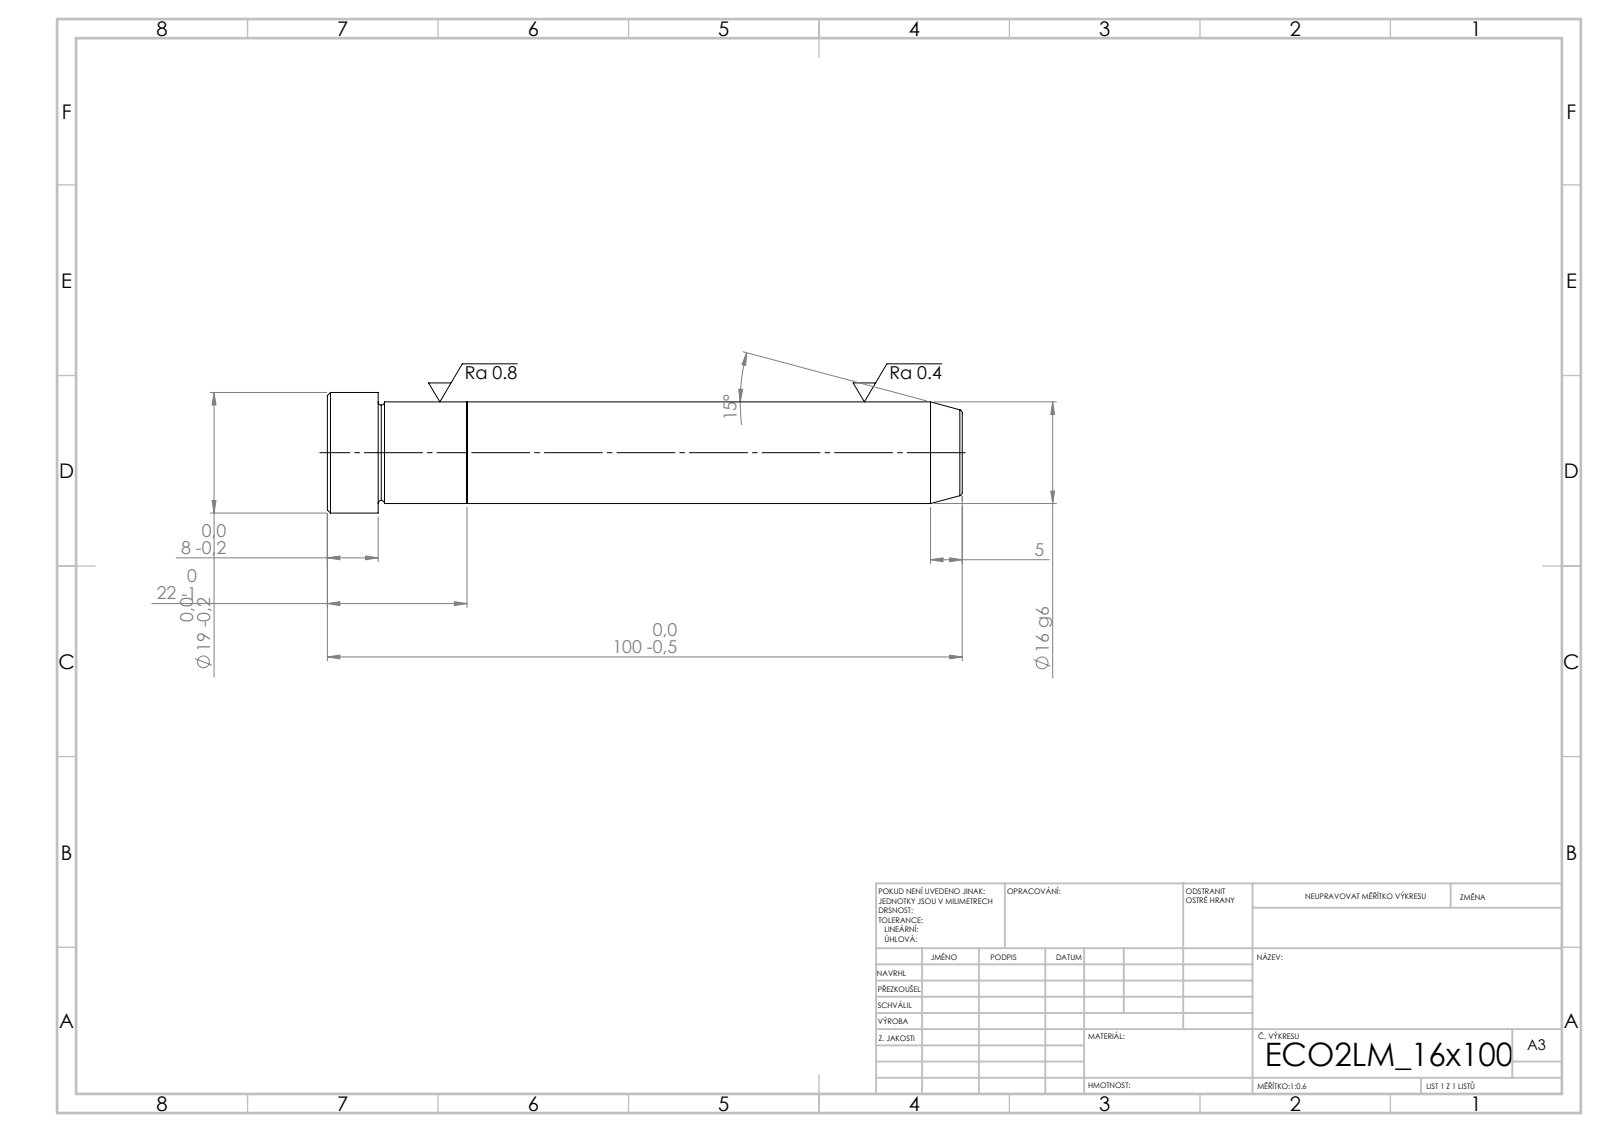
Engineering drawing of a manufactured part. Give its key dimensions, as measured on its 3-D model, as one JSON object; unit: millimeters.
{"step_written_by": "SolidWorks 2019 (CONFIG_CONTROL_DESIGN)", "units": "millimeters", "bodies": {"solids": 2, "faces": 21, "planar": 5, "cylindrical": 6, "other": 10}, "overall_size": [100, 19, 19], "volume_mm3": 20579, "surface_area_mm2": 5999, "round_bosses_or_shafts": [[19, 1], [16, 1]], "face_to_face_distances": [22, 78, 100, 92, 14, 8]}
